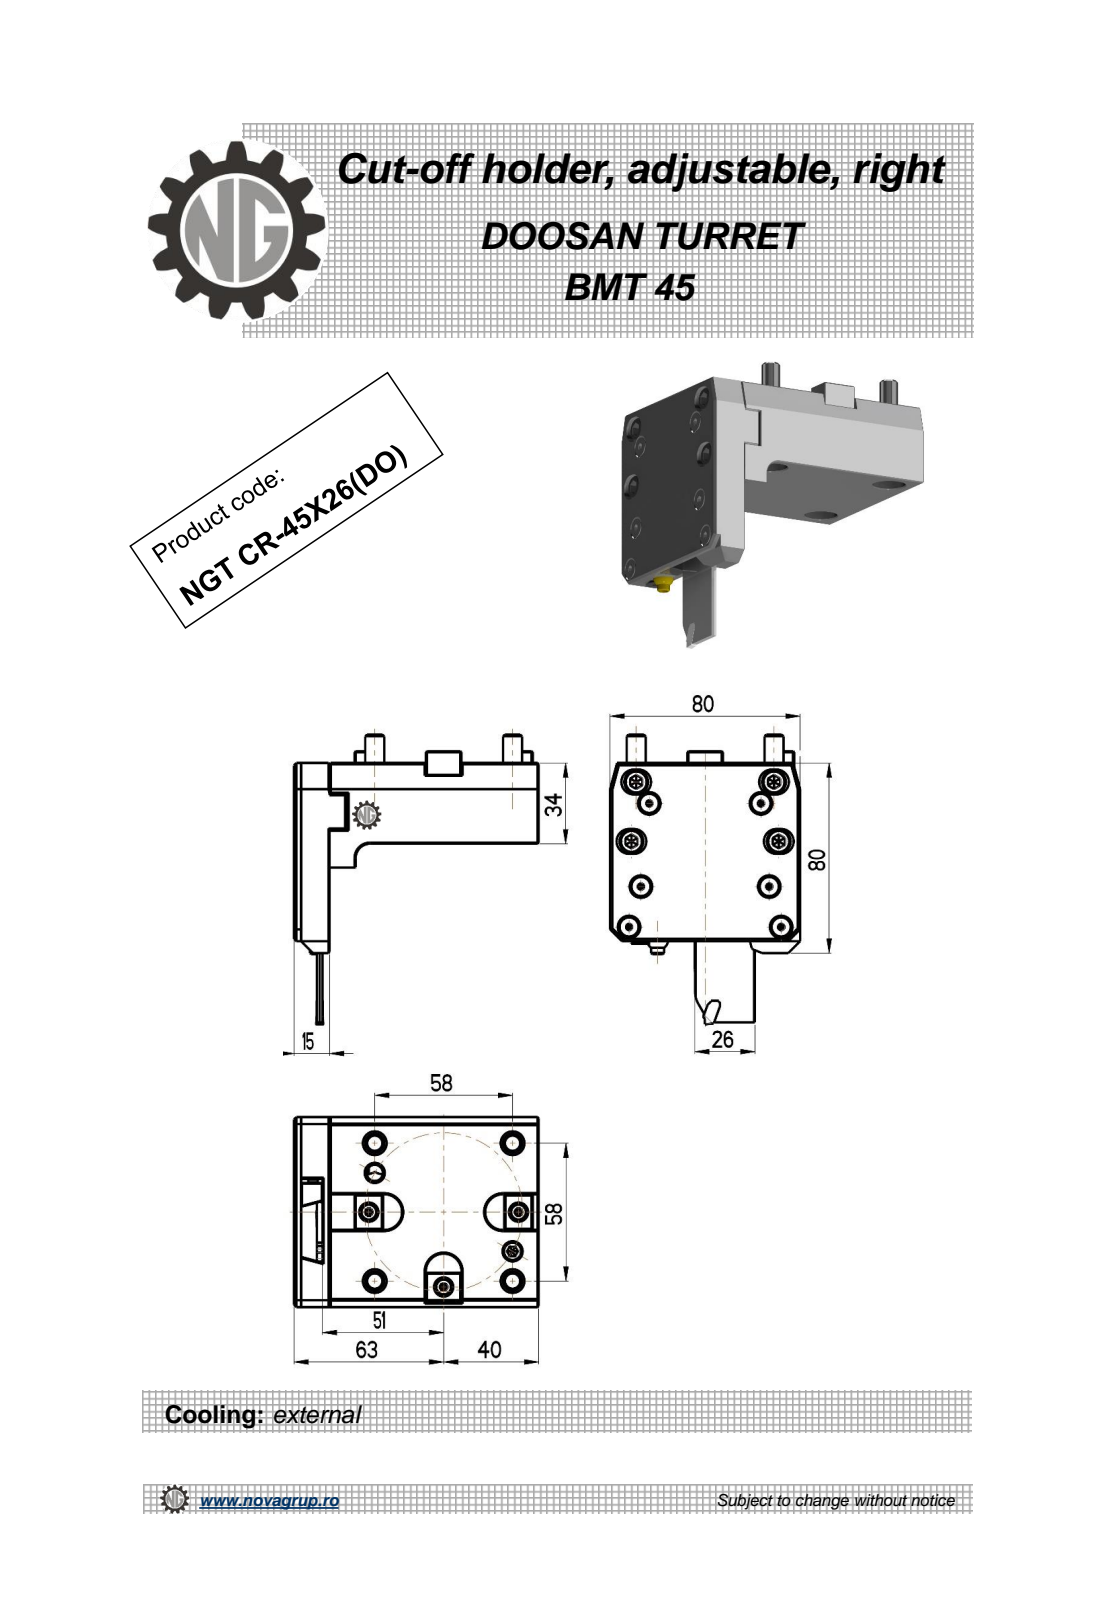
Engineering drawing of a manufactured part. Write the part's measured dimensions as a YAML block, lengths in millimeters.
part_name: "NGT_CR_45_26_DO"
step_written_by: "PRO/ENGINEER BY PARAMETRIC TECHNOLOGY CORPORATION, 2010280 (CONFIG_CONTROL_DESIGN)"
units: millimeters
bodies: {solids: 1, faces: 406, planar: 263, cylindrical: 79, other: 64}
overall_size: [103, 92.45, 80]
volume: 311803
surface_area: 52076
round_holes:
  - {diameter: 3.5, count: 1}
  - {diameter: 6.8, count: 1}
round_bosses_or_shafts:
  - {diameter: 8, count: 5}
  - {diameter: 10, count: 4}
  - {diameter: 4, count: 3}
  - {diameter: 5.5, count: 1}
partial_cylinders:
  - {radius: 0.2, count: 24}
  - {radius: 5.25, count: 8}
  - {radius: 0.16, count: 6}
  - {radius: 0.41, count: 6}
  - {radius: 7.5, count: 3}
  - {radius: 6, count: 1}
  - {radius: 60, count: 1}
  - {radius: 125, count: 1}
face_to_face_distances: [34, 12, 3, 15, 80, 88, 103, 100, 91, 9]
hole_center_spacings: [24.75]
